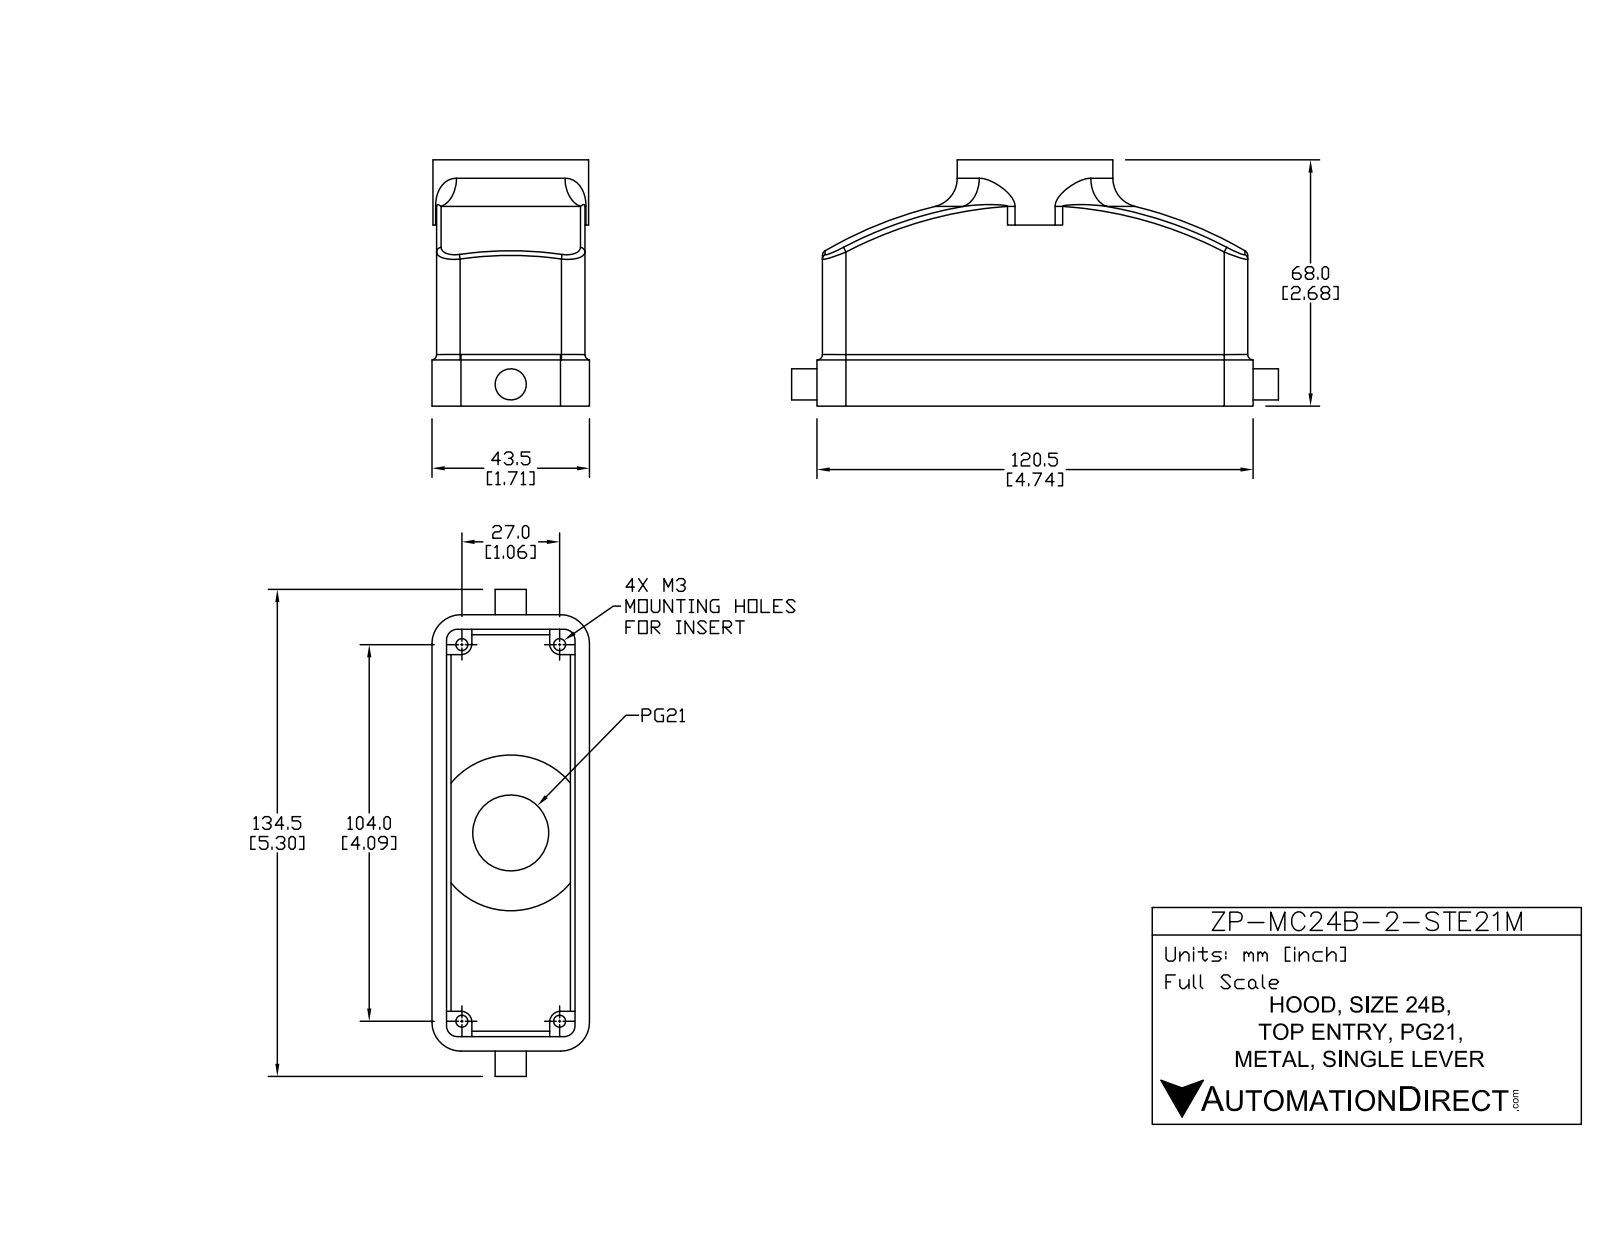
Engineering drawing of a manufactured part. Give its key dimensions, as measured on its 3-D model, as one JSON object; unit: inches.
{"part_name": "ZP-MC24B-2-STE21M", "step_written_by": "SolidWorks 2011 (AUTOMOTIVE_DESIGN)", "units": "inches", "bodies": {"solids": 2, "faces": 108, "planar": 41, "cylindrical": 39, "other": 28}, "overall_size": [5.295, 2.677, 1.713], "volume_in3": 5.511, "surface_area_in2": 64.72, "round_holes": [[0.13, 4], [0.827, 1], [1.063, 1]], "round_bosses_or_shafts": [[1.693, 1], [0.339, 1]], "partial_cylinders_radius": [[0.118, 8], [0.315, 8], [0.059, 4], [0.217, 4], [0.256, 4]], "face_to_face_distances": [0.157, 1.457, 0.049, 1.506, 1.614, 1.299, 0.207, 1.663, 1.555, 0.108], "hole_center_spacings": [2.115, 1.063, 4.094, 4.23]}
